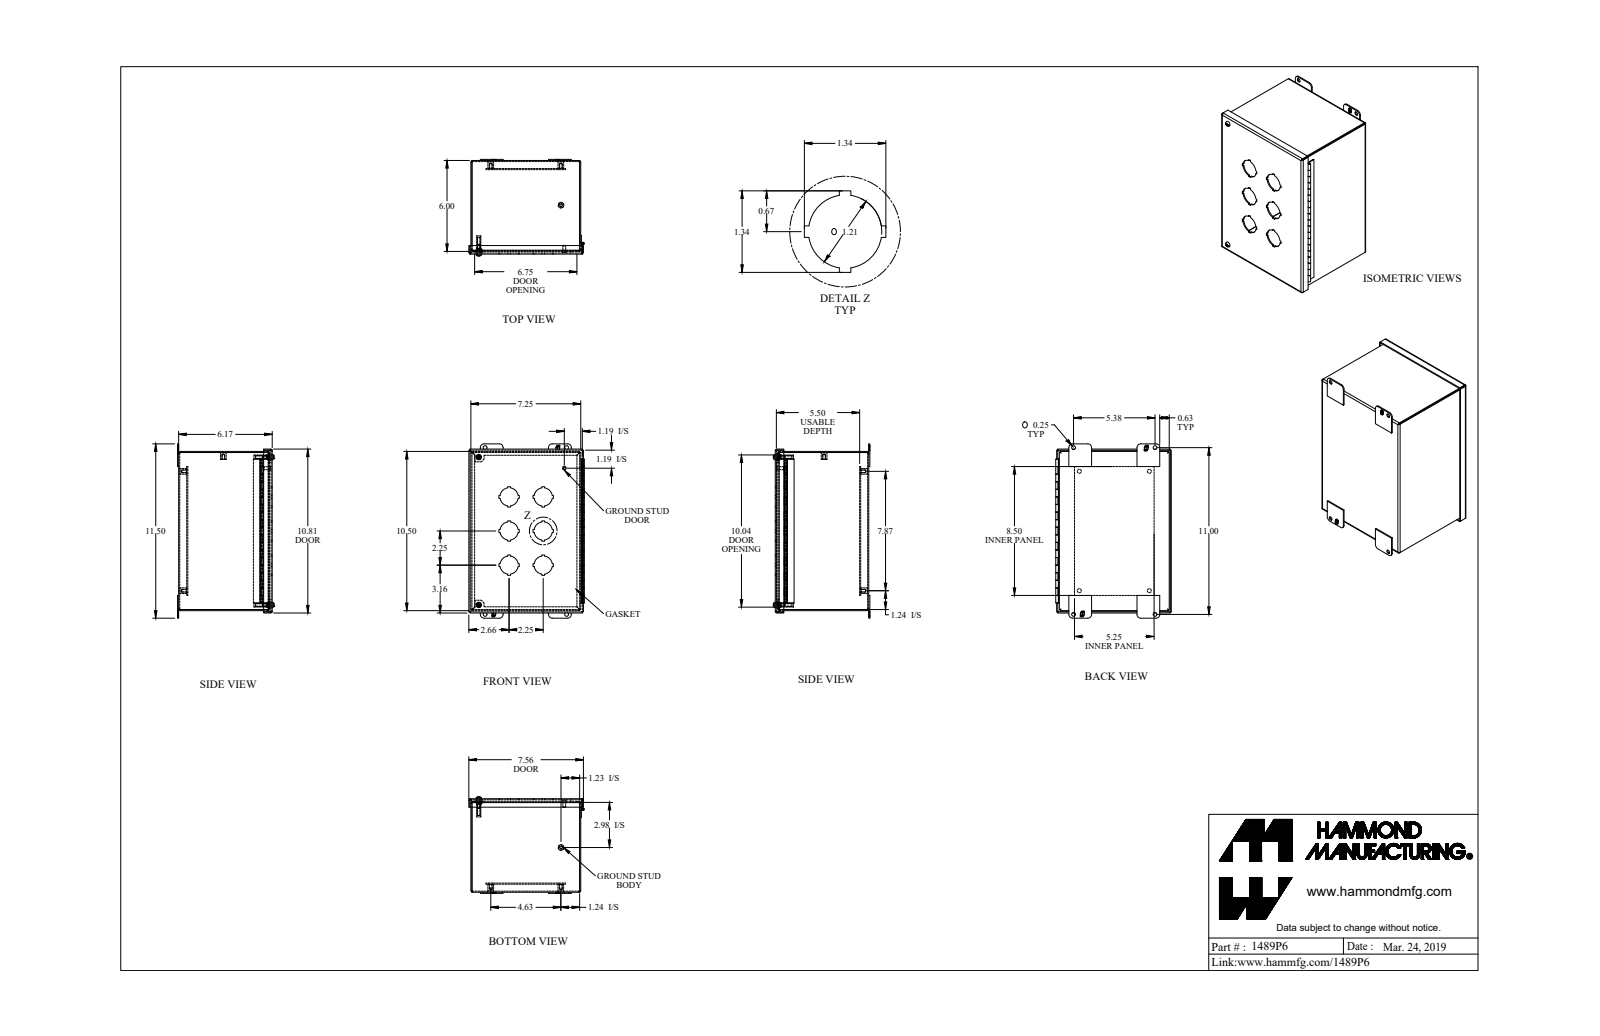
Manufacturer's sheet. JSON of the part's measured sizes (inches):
{"part_name": "1489P6_Default", "step_written_by": "SolidWorks 2019 (CONFIG_CONTROL_DESIGN)", "units": "inches", "bodies": {"solids": 21, "faces": 788, "planar": 536, "cylindrical": 194, "other": 58}, "overall_size": [11.5, 7.623, 6.371], "volume_in3": 36.61, "surface_area_in2": 977.8, "round_holes": [[0.25, 6], [1.21, 6], [0.156, 5], [0.265, 4], [0.159, 2], [0.406, 2]], "round_bosses_or_shafts": [[0.375, 4], [0.39, 2], [0.275, 2], [0.19, 2], [0.148, 2], [0.375, 1], [0.25, 1], [0.188, 1]], "partial_cylinders_radius": [[0.036, 12], [0.108, 12], [0.25, 8], [0.16, 2], [0.171, 2], [0.125, 1]], "face_to_face_distances": [0.072, 6.1, 7.178, 5.568, 0.532, 10.428, 6.172, 6.028, 7.25, 7.106], "hole_center_spacings": [4.625, 5.239, 10.68, 2.25, 9.75, 1.607, 1.607, 2.051]}
